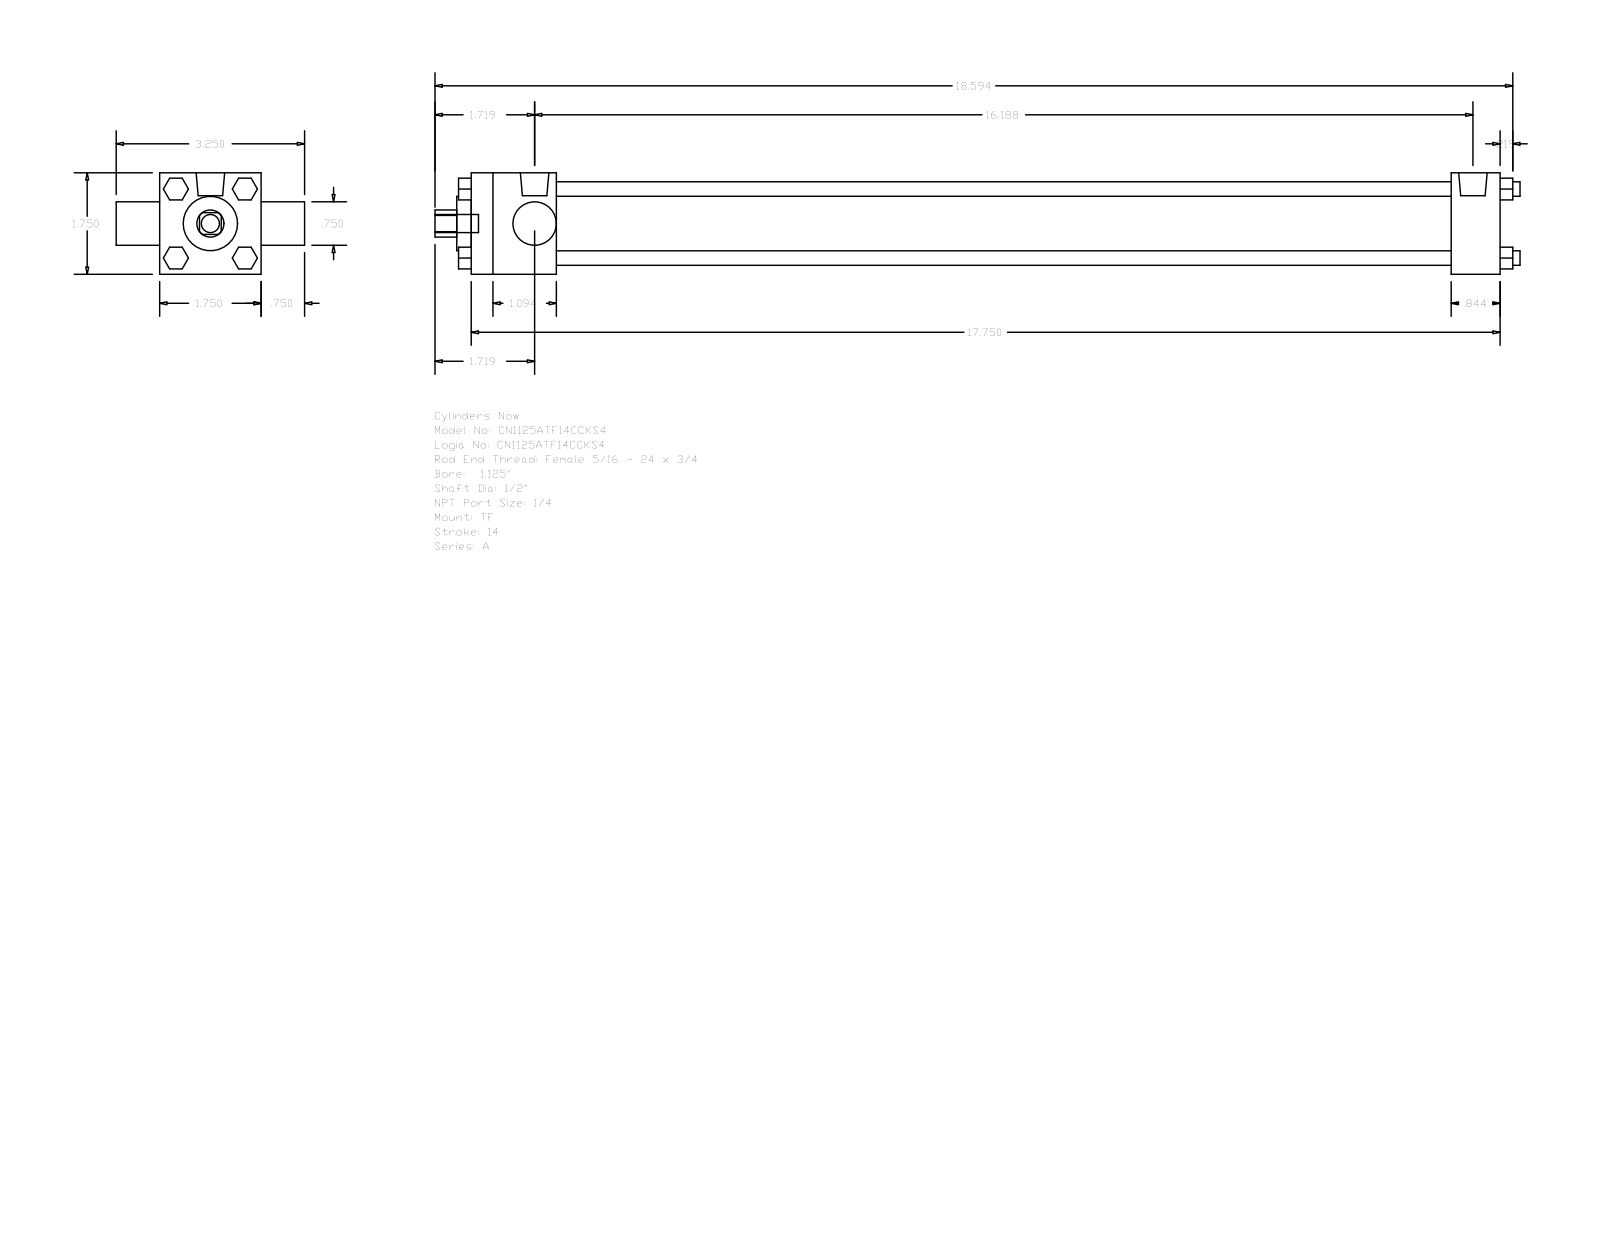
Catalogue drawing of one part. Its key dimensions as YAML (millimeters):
part_name: "A_TF__0112_0.5"
step_written_by: "GSSL Pune (CONFIG_CONTROL_DESIGN)"
units: millimeters
bodies: {solids: 0, faces: 120, planar: 92, cylindrical: 28, other: 0}
overall_size: [475.46, 82.55, 44.45]
round_holes:
  - {diameter: 12.7, count: 1}
  - {diameter: 19.05, count: 1}
  - {diameter: 23.81, count: 1}
  - {diameter: 31.88, count: 1}
round_bosses_or_shafts:
  - {diameter: 6.35, count: 4}
  - {diameter: 5.56, count: 3}
  - {diameter: 12.49, count: 2}
  - {diameter: 7.94, count: 1}
partial_cylinders:
  - {radius: 5.94, count: 1}
face_to_face_distances: [44.46, 450.85, 429.41, 21.44, 37.3, 392.11, 413.55, 19.04, 63.5, 9.53]
